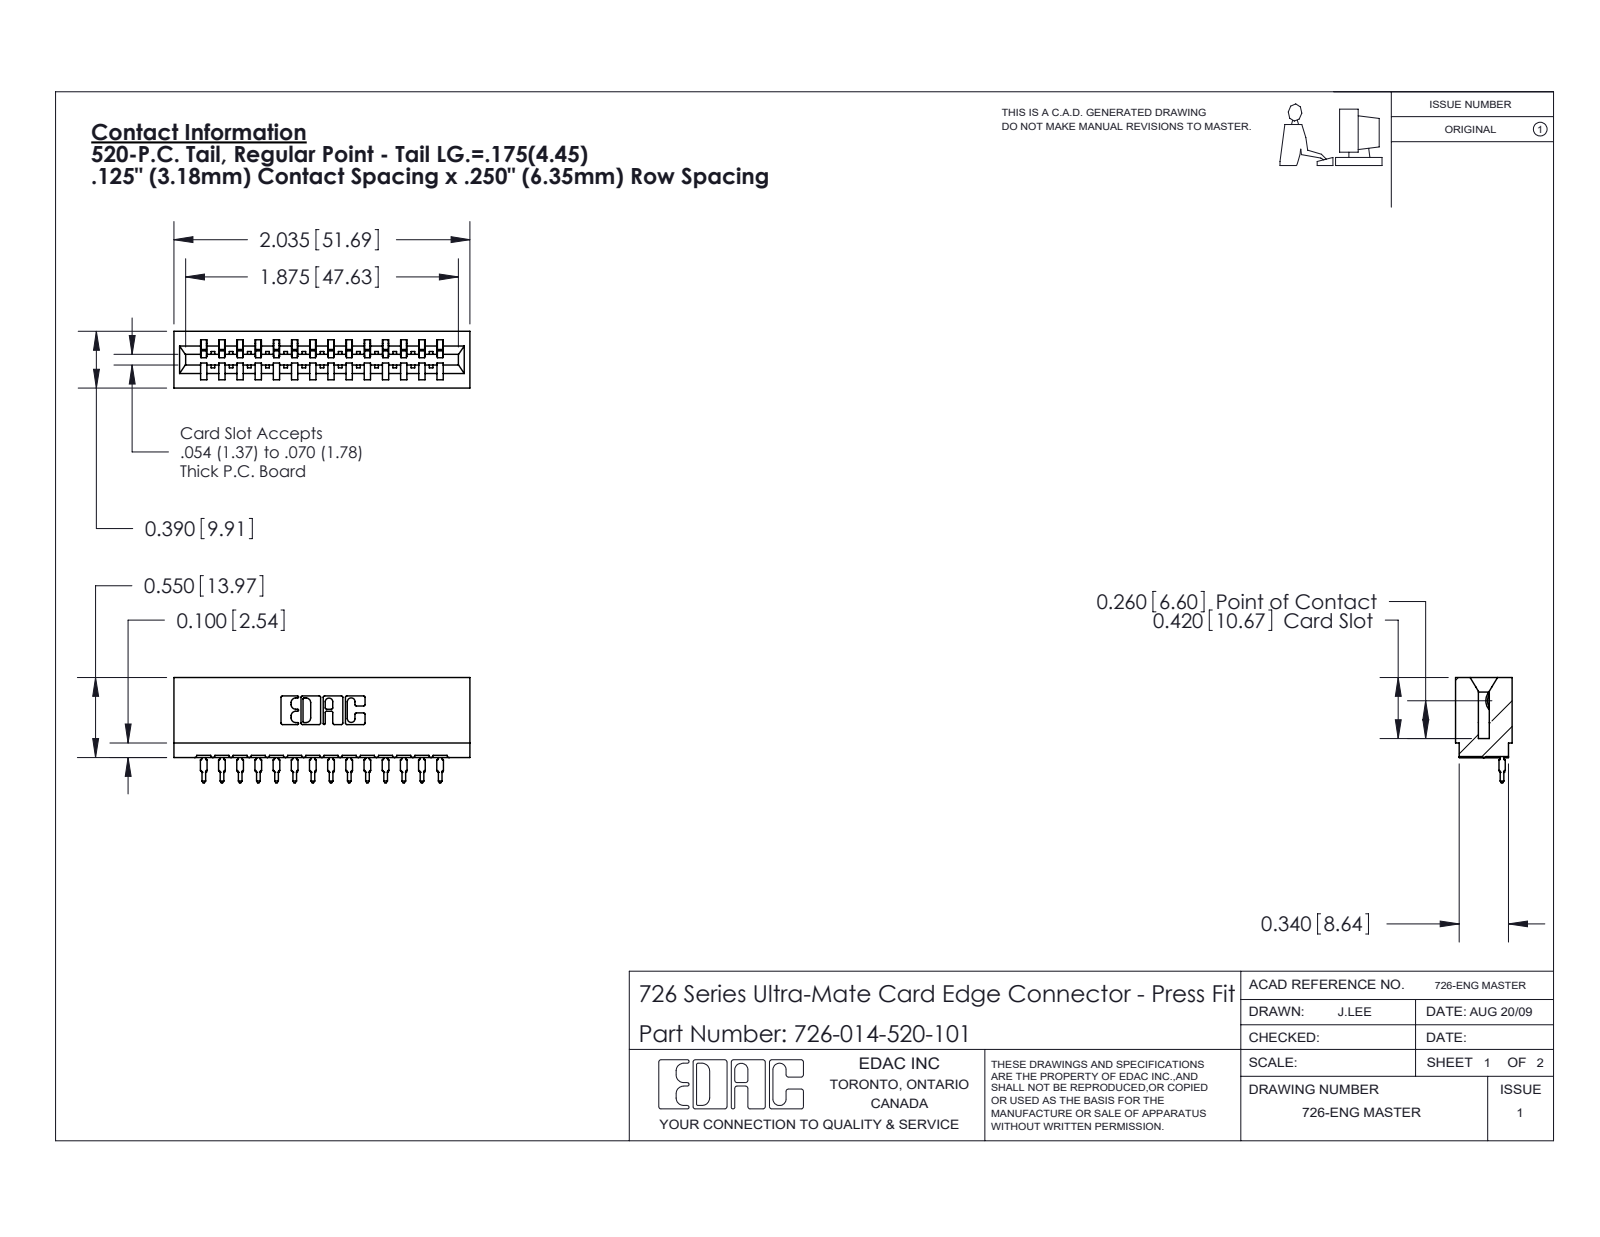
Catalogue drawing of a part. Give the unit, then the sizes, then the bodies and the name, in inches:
Units: inches
Overall size (bounding box): 2.035 × 0.724 × 0.39
Partial cylindrical surfaces — rounded edges, fillets, slot ends (radius × count): R0.021 ×28, R0.01 ×22, R0.015 ×15, R0.007 ×6, R0.031 ×6, R0.005 ×4, R0.011 ×4, R0.026 ×3
Main face-to-face distances: 0.25, 0.057, 0.333, 0.39, 0.125, 0.025, 0.75, 1.25, 0.5, 0.307
Volume: 0.29 in³ · Surface area: 10.46 in²
Bodies: 15 solids, 1609 faces (937 planar, 308 cylindrical, 364 other)
Part name (STEP PRODUCT): 726 Part_.515 Slot Depth - 01; 746-292-001_520; 726-014-520-101
STEP written by: SolidWorks 2020 (CONFIG_CONTROL_DESIGN)
